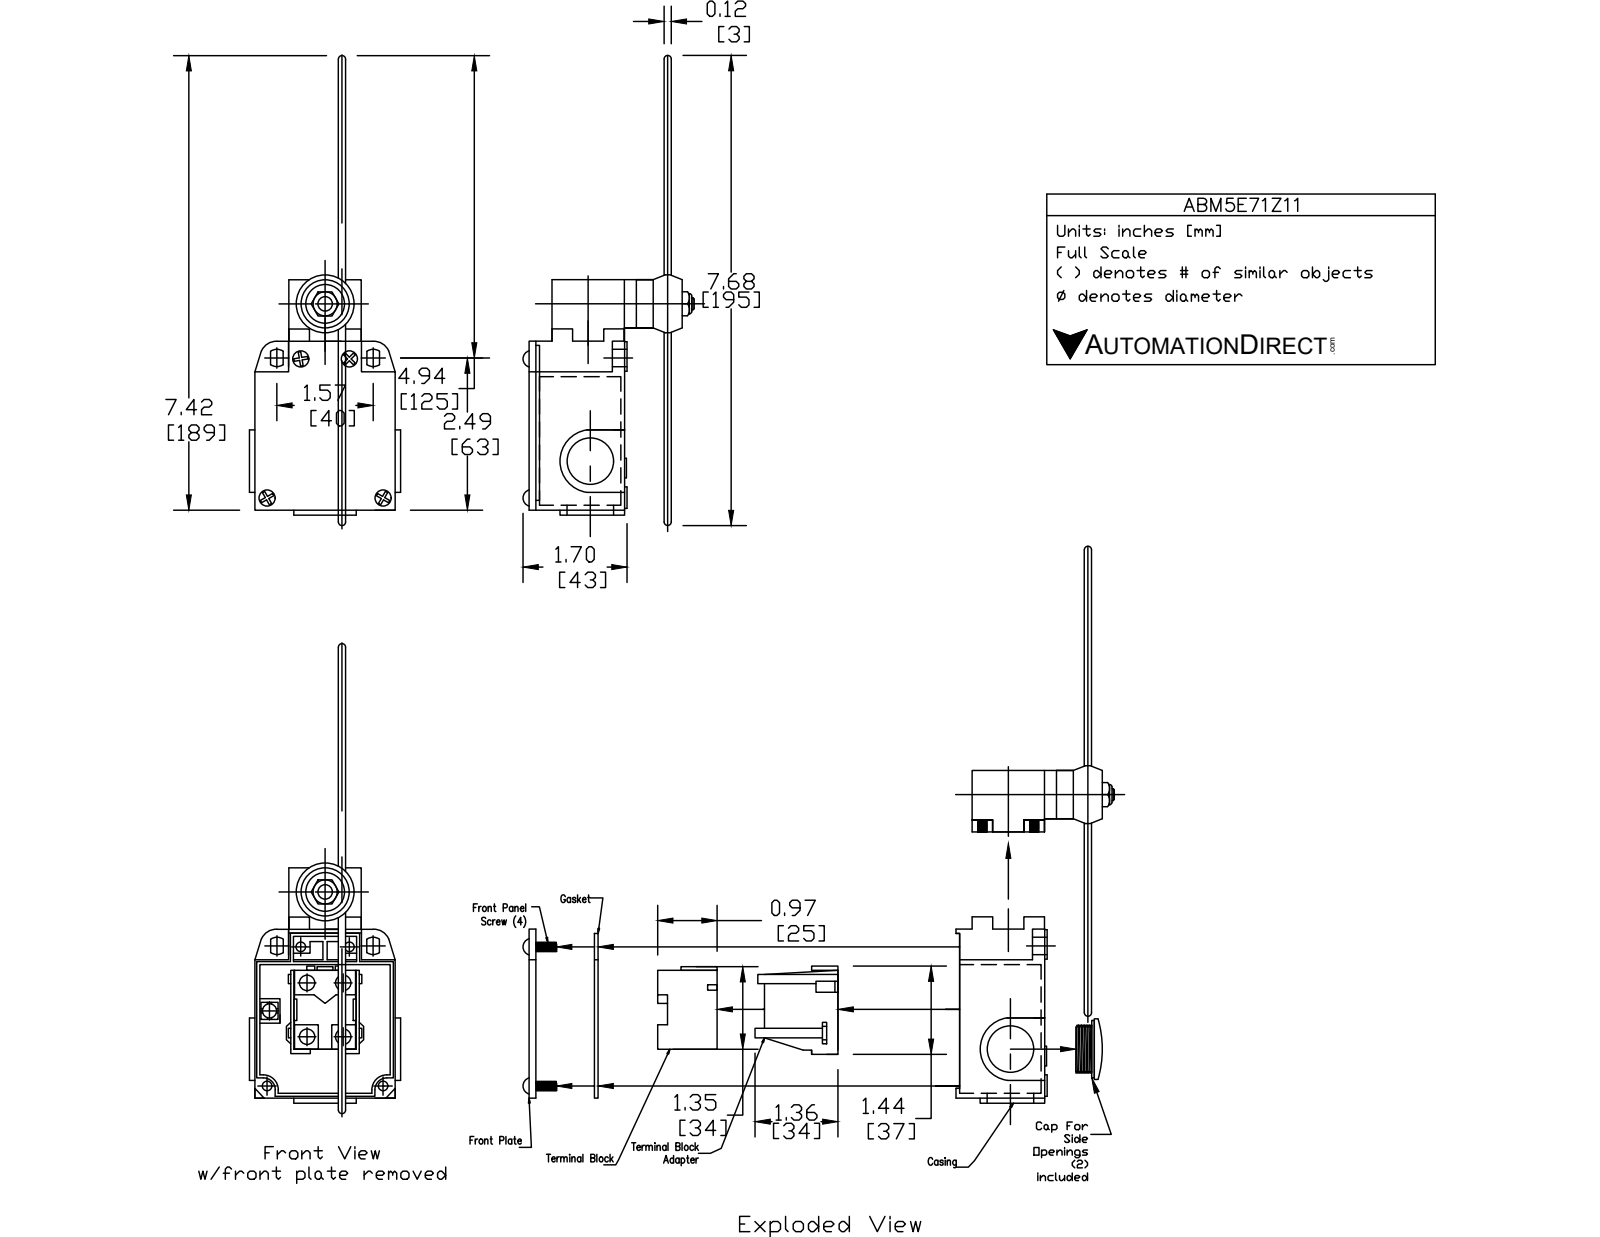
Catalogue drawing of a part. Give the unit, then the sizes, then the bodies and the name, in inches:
Units: inches
Overall size (bounding box): 7.672 × 2.335 × 1.575
Round holes (diameter × count): ⌀0.205 ×2, ⌀0.118 ×1, ⌀0.236 ×1, ⌀0.551 ×1, ⌀0.669 ×1, ⌀0.748 ×1
Round bosses / shafts (diameter × count): ⌀0.394 ×5, ⌀0.276 ×2, ⌀0.945 ×1, ⌀0.787 ×1, ⌀0.236 ×1
Partial cylindrical surfaces — rounded edges, fillets, slot ends (radius × count): R0.059 ×16, R0.039 ×4, R0.197 ×4, R0.128 ×2, R0.453 ×1, R0.472 ×1
Main face-to-face distances: 1.575, 1.555, 0.197, 1.181, 1.378, 3.012, 0.984, 0.374, 0.177, 4.016
Hole centre spacings: 1.394, 0.551, 1.048, 2.641, 3.282
Volume: 8.642 in³ · Surface area: 45.88 in²
Bodies: 5 solids, 238 faces (116 planar, 89 cylindrical, 33 other)
Part name (STEP PRODUCT): ABM5E71Z11
STEP written by: SolidWorks 2017 (AUTOMOTIVE_DESIGN)
